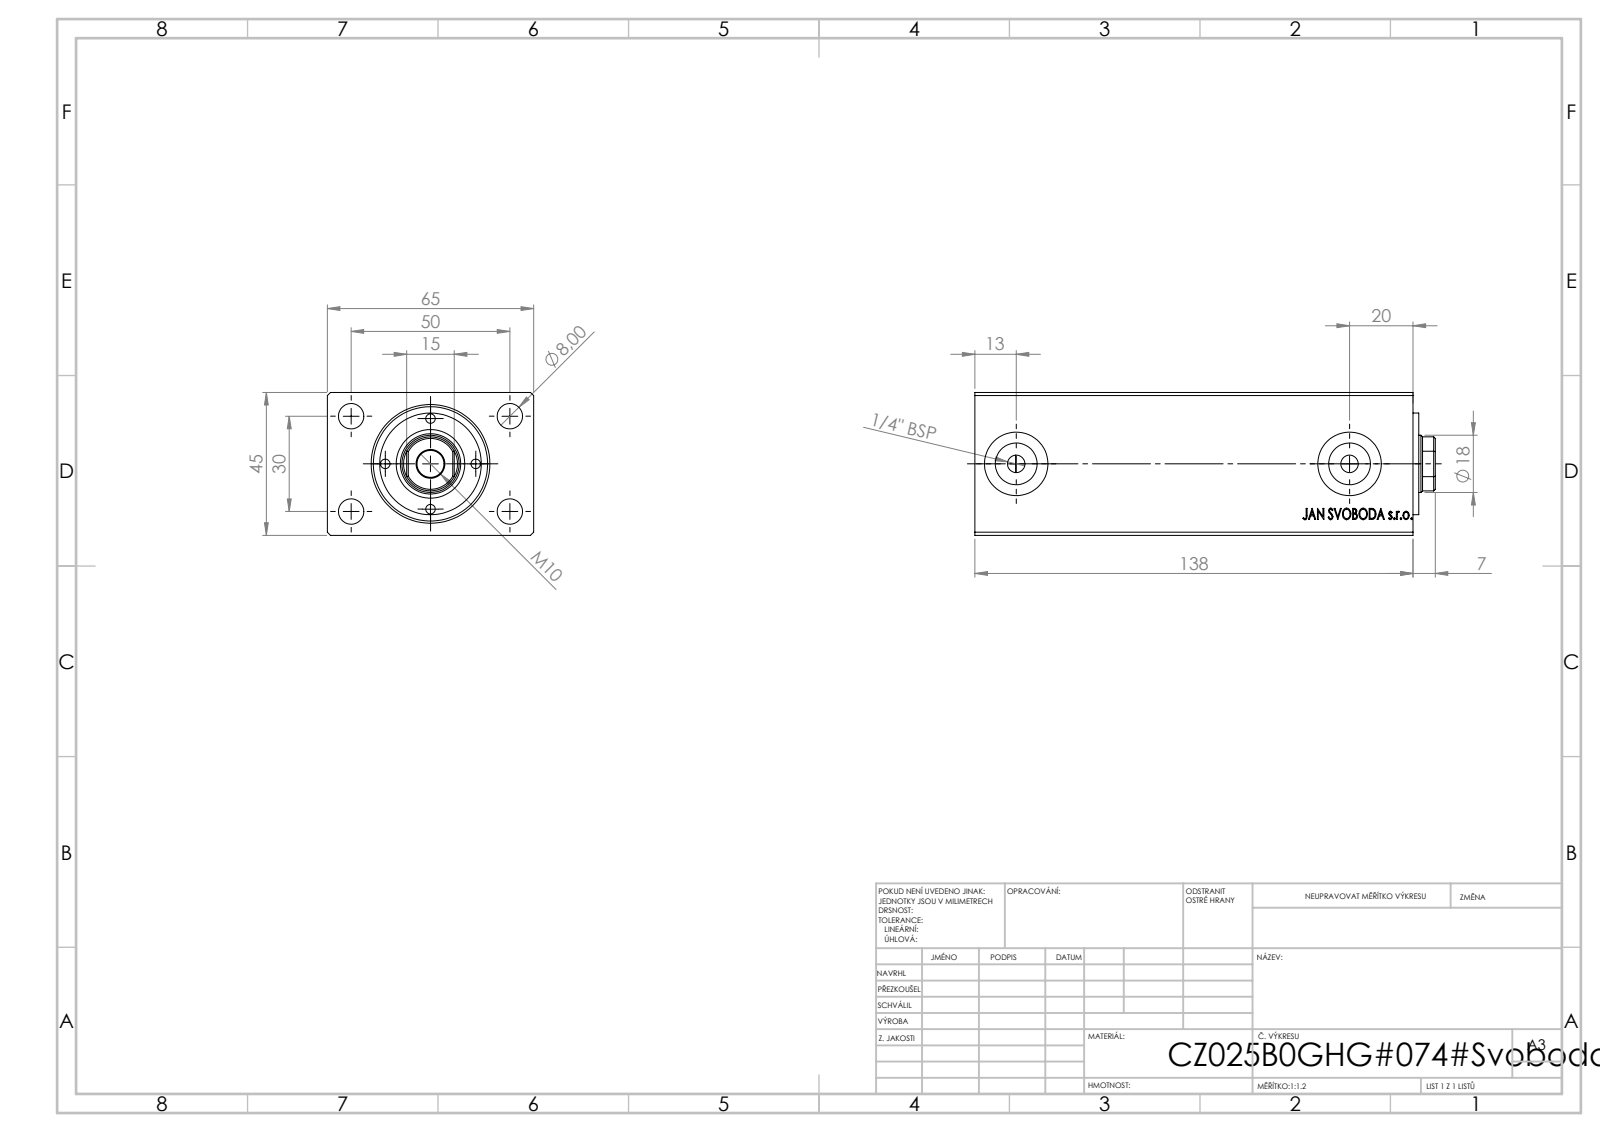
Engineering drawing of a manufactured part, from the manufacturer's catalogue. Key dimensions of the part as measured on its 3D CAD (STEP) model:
Part name (STEP PRODUCT): V500CZ; V500CZ_B_VC
STEP written by: SolidWorks 2019 (CONFIG_CONTROL_DESIGN)
Units: millimetres
Bodies: 3 solids, 873 faces (399 planar, 58 cylindrical, 416 other)
Overall size (bounding box): 145 × 65 × 45
Volume: 371 621 mm³ · Surface area: 64 838 mm²
Round holes (diameter × count): ⌀3 ×4, ⌀8 ×4, ⌀5.5 ×2, ⌀13.16 ×2, ⌀20 ×2, ⌀8.5 ×1, ⌀18 ×1, ⌀19 ×1, ⌀25 ×1, ⌀36 ×1
Round bosses / shafts (diameter × count): ⌀32 ×1
Partial cylindrical surfaces — rounded edges, fillets, slot ends (radius × count): R8.5 ×1
Main face-to-face distances: 45, 65, 138, 7, 137.8, 125.2, 12.6, 12.8, 1.8, 5.2
Hole centre spacings: 14.25, 18.45, 20.15, 25.01, 29.15, 38.48, 42.02, 28.5
